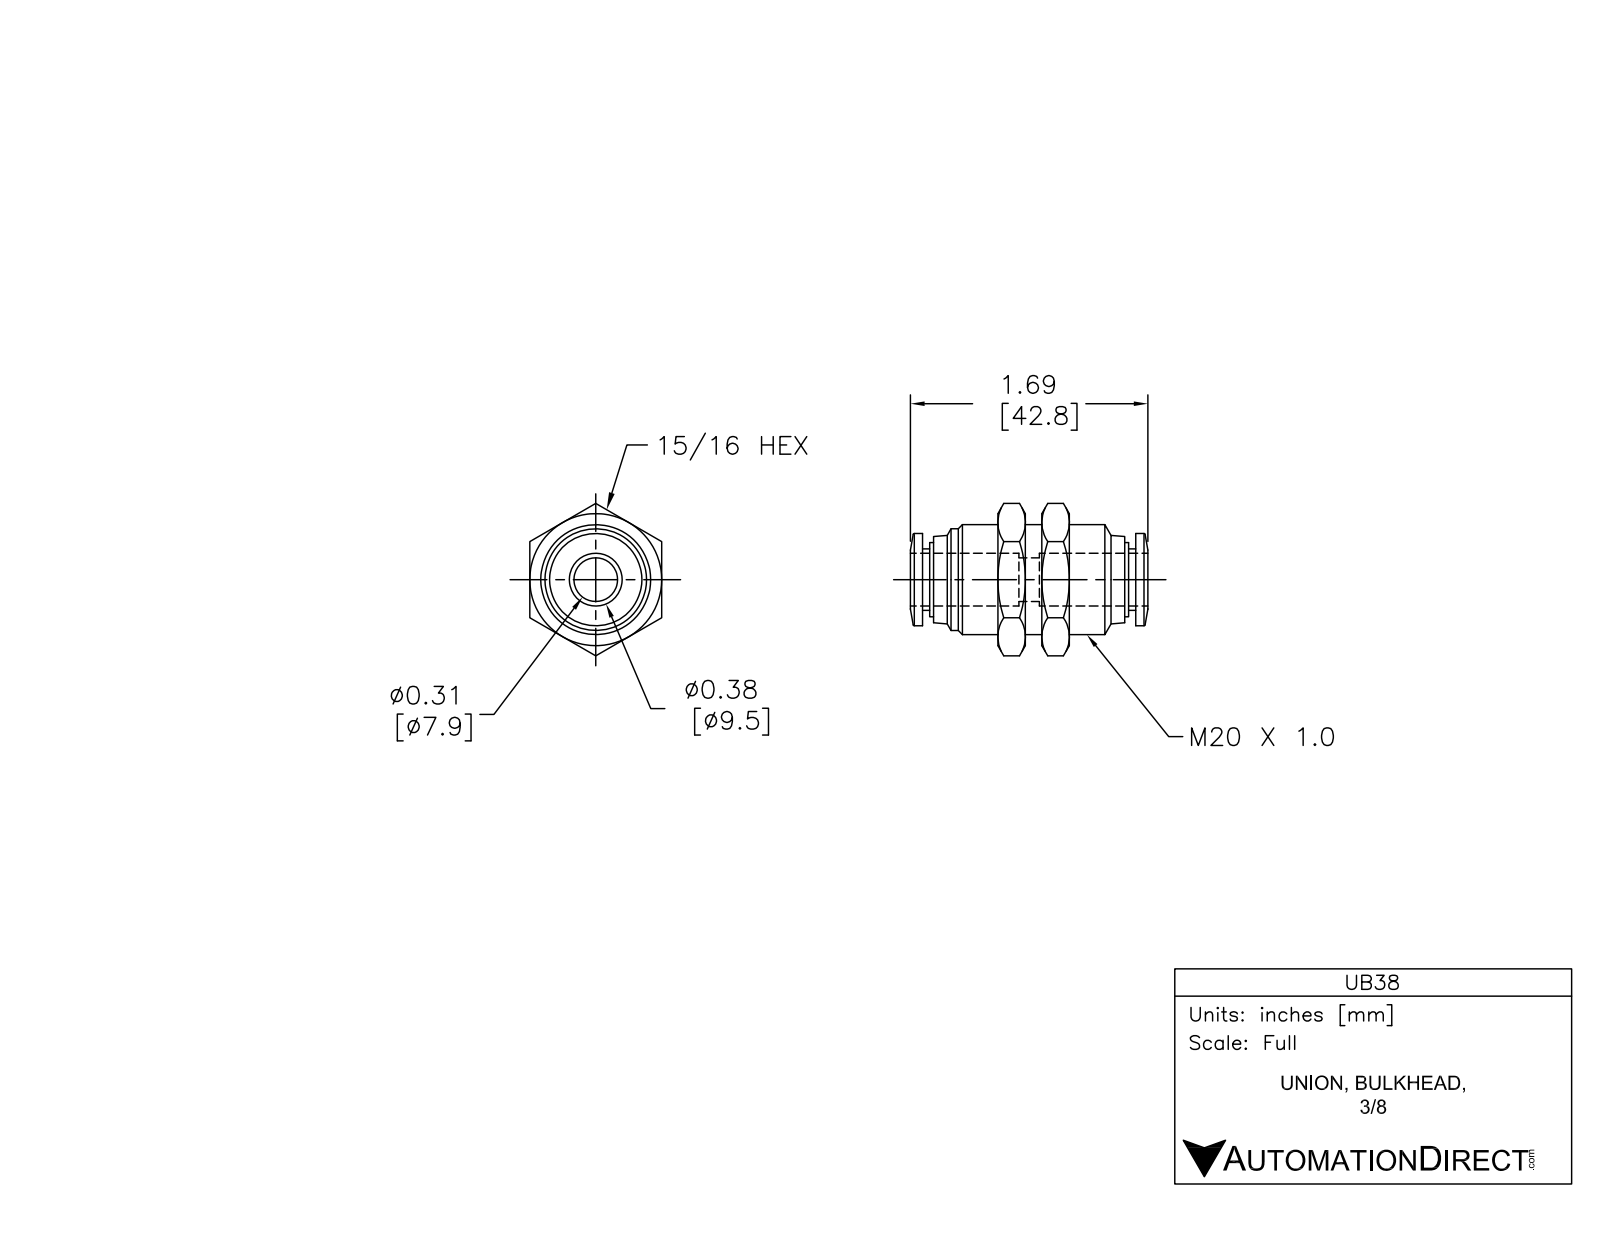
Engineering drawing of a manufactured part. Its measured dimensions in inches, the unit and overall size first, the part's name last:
Units: inches
Overall size (bounding box): 1.701 × 1.091 × 0.945
Round holes (diameter × count): ⌀0.315 ×1, ⌀0.386 ×1
Round bosses / shafts (diameter × count): ⌀0.787 ×1, ⌀0.728 ×1, ⌀0.661 ×1, ⌀0.531 ×1, ⌀0.441 ×1
Main face-to-face distances: 0.945, 0.197, 0.315, 0.508, 0.705, 0.823, 1.02, 0.118, 0.512, 1.528
Volume: 0.619 in³ · Surface area: 8.475 in²
Bodies: 1 solid, 100 faces (24 planar, 26 cylindrical, 50 other)
Part name (STEP PRODUCT): UB38
STEP written by: SolidWorks 2015 (AUTOMOTIVE_DESIGN)
